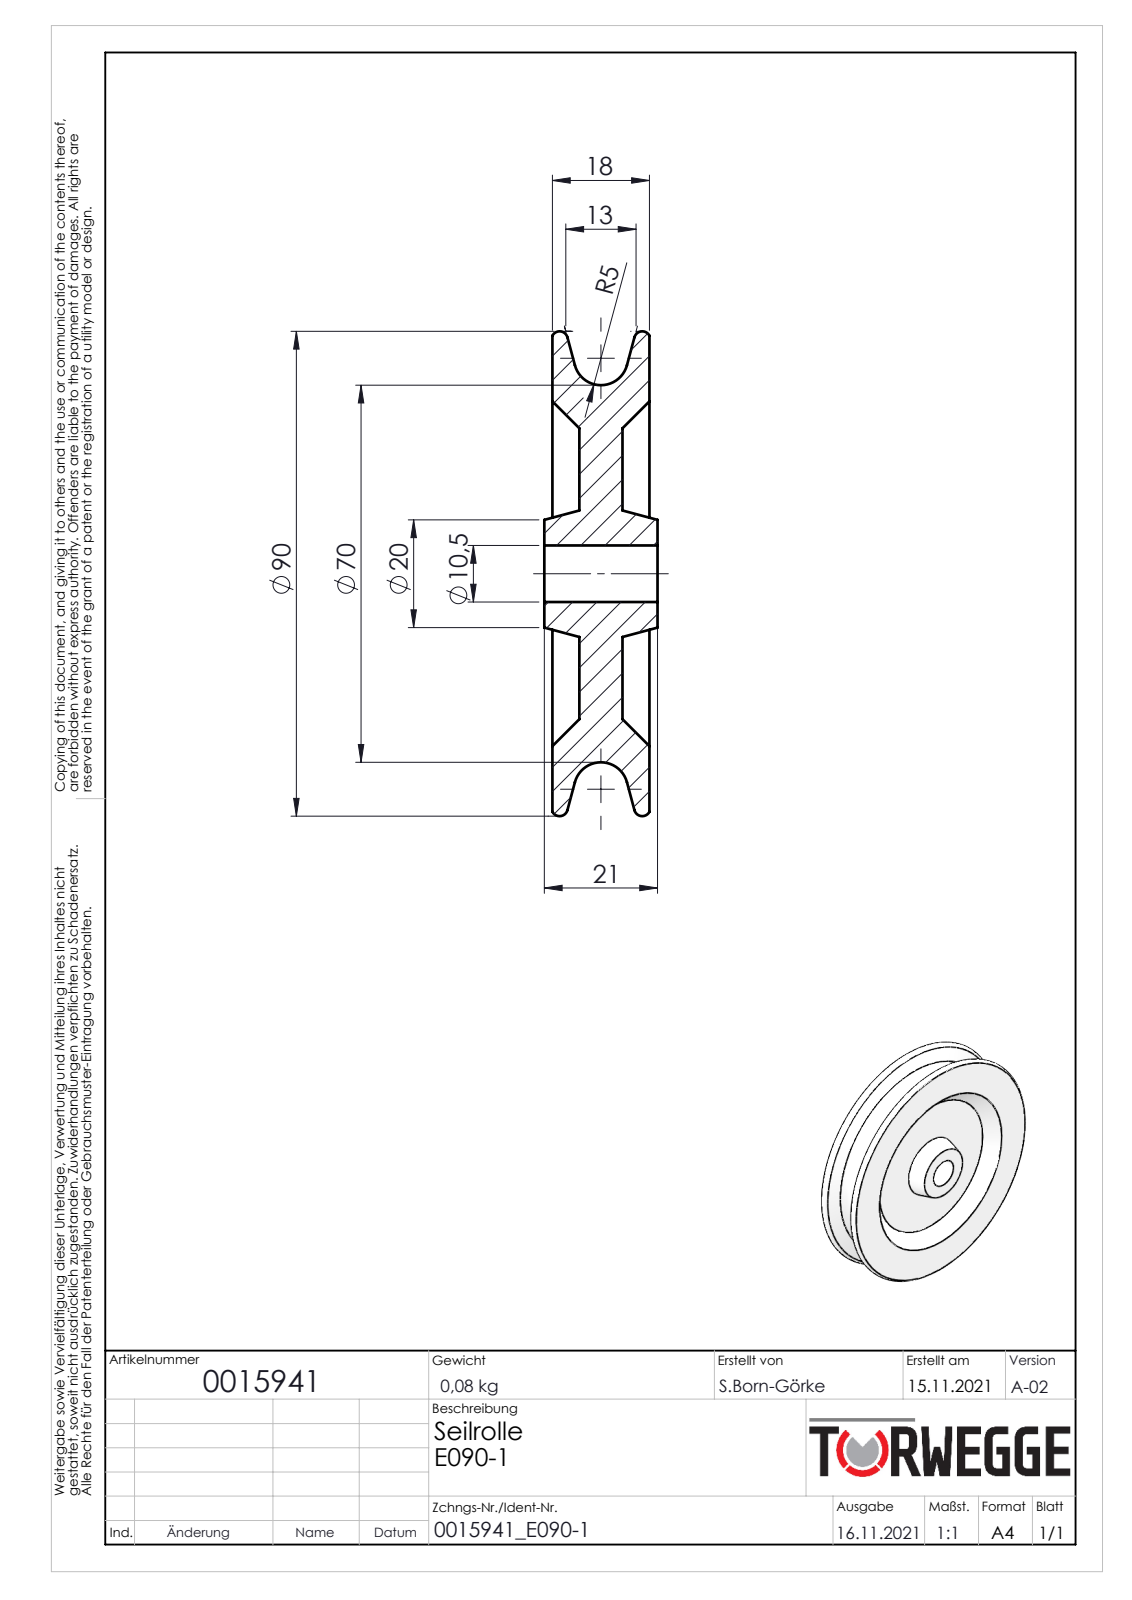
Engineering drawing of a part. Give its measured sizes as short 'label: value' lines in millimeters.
name: 0015941
written by: SolidWorks 2020 (AUTOMOTIVE_DESIGN)
unit: mm
bodies: 1 solid, 28 faces (6 planar, 2 cylindrical, 20 other)
size: 90 × 90 × 21
volume: 64 778 mm³; area: 22 031 mm²
holes: 1× ⌀10.5
face distances: 5, 13, 18, 8, 1.5, 6.5, 14.5, 19.5, 21
